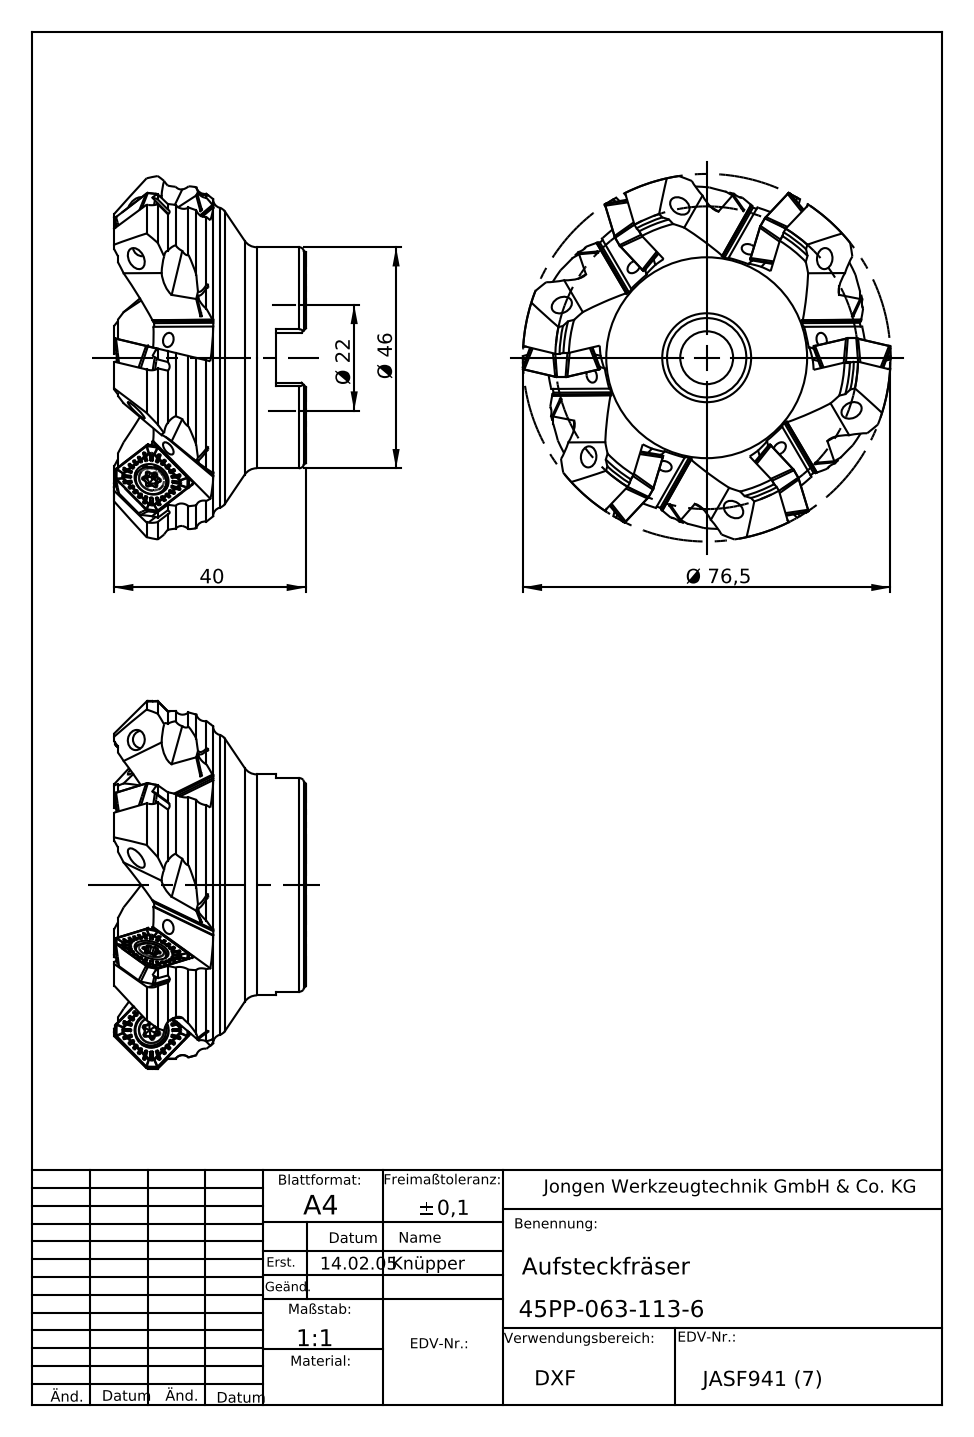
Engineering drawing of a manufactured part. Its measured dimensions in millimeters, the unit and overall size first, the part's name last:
Units: millimetres
Overall size (bounding box): 76.51 × 76.51 × 40
Round holes (diameter × count): ⌀3 ×6, ⌀11 ×1, ⌀16.5 ×1, ⌀22 ×1, ⌀22.15 ×1, ⌀22.3 ×1
Round bosses / shafts (diameter × count): ⌀46 ×1
Partial cylindrical surfaces — rounded edges, fillets, slot ends (radius × count): R1.5 ×6, R1.5 ×6, R2.55 ×6, R36.16 ×1
Main face-to-face distances: 31.4, 6.3, 25.1, 20, 13.7, 11.4, 10.4, 24.2, 17.9, 4.2
Volume: 89 041 mm³ · Surface area: 18 330 mm²
Bodies: 1 solid, 259 faces (125 planar, 53 cylindrical, 81 other)
Part name (STEP PRODUCT): 45PP-063-113-6
STEP written by: SolidWorks 2013 (AUTOMOTIVE_DESIGN)
